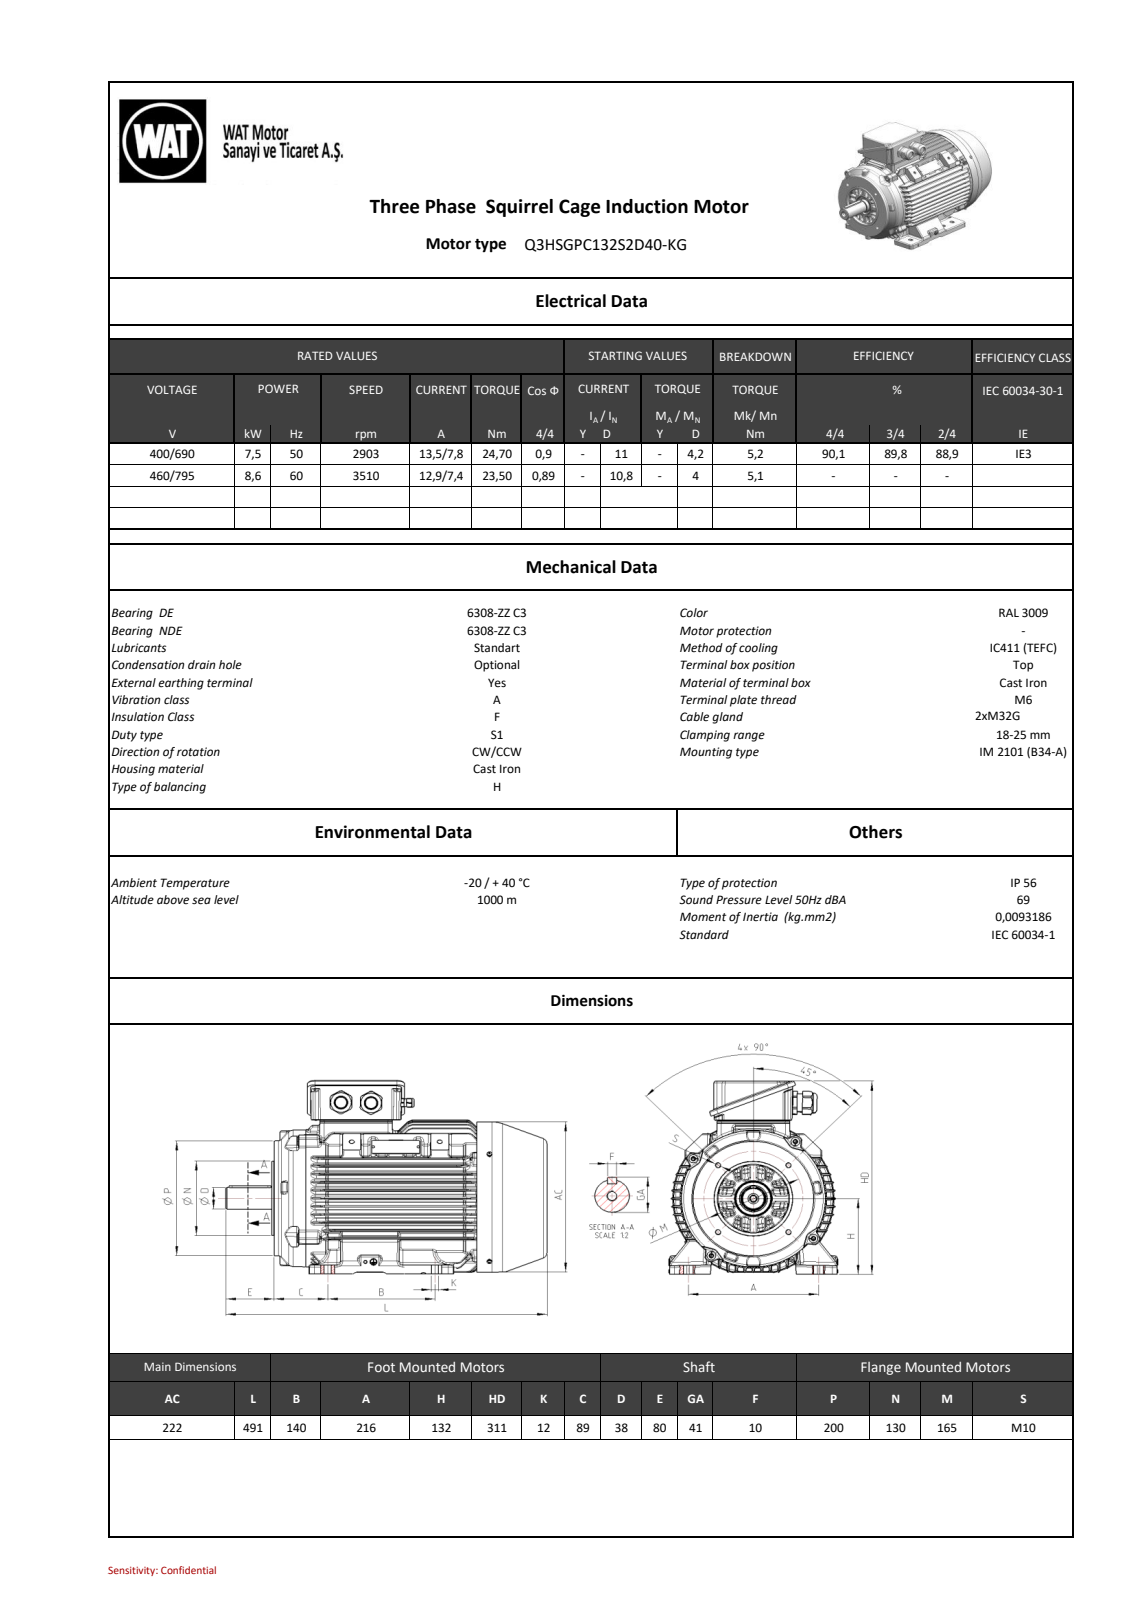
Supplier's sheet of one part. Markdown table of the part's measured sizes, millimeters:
| quantity | value |
| --- | --- |
| part name | 26000A30F4D8rozp |
| STEP written by | SIEMENS PLM Software NX 11.0 (AUTOMOTIVE_DESIGN) |
| units | millimeters |
| bodies | 0 solids, 5393 faces (1040 planar, 1523 cylindrical, 2830 other) |
| overall size | 491 × 311.13 × 275 |
| round holes (diameter × count) | 5 × 7, 8.5 × 4, 2.5 × 2, 6.8 × 2, 10 × 2, 17.2 × 2, 6 × 1, 6.3 × 1, 8 × 1, 10.2 × 1, 11.3 × 1, 13 × 1 |
| round bosses / shafts (diameter × count) | 10 × 4, 8.65 × 4, 8 × 4, 4 × 4, 27.7 × 2, 25.25 × 2, 20 × 2, 215 × 1 |
| partial cylindrical surfaces (radius × count) | 4 × 320, 3 × 138, 0.5 × 118, 1.5 × 96, 2 × 30, 1 × 29, 6 × 28, 1.8 × 24 |
| main face-to-face distances | 13.1, 13.18, 26.28, 39.54, 26.44, 13.26, 90.54, 52.86, 39.76, 26.58 |
| hole center spacings | 21.29, 97, 115.92, 137.83, 178.83, 82.51, 116.68, 137.18 |
